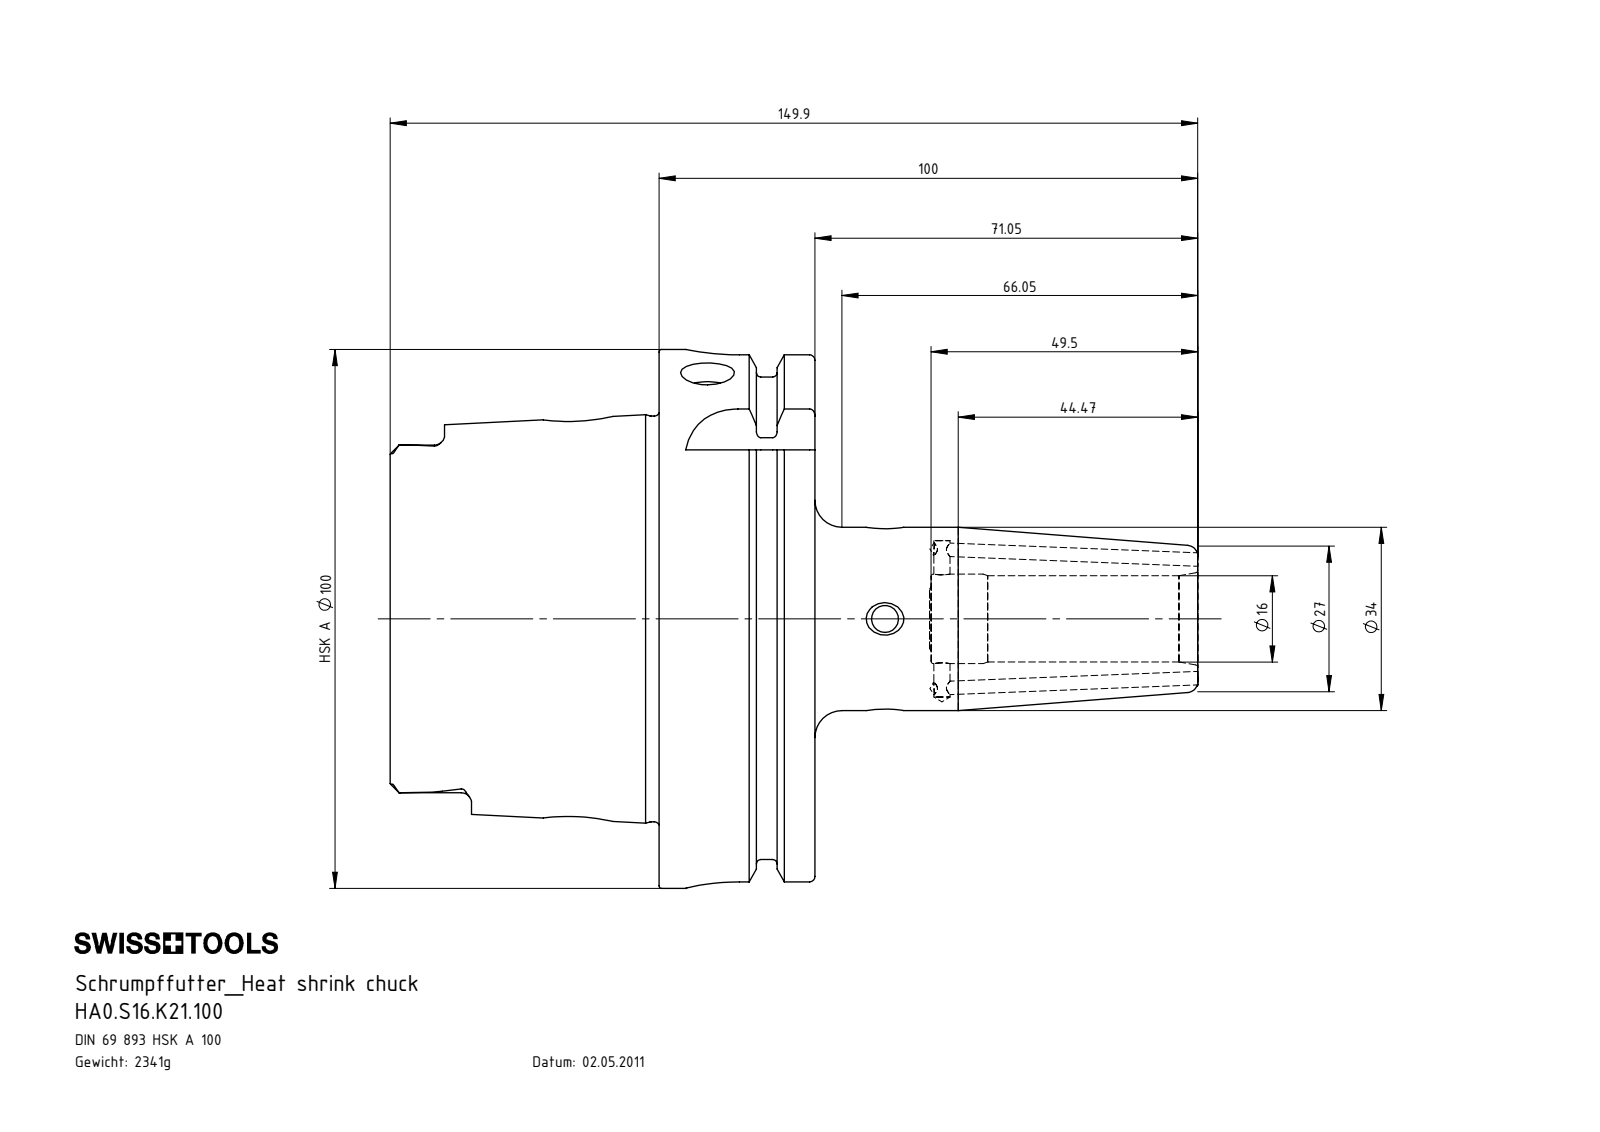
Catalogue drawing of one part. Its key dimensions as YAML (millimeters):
part_name: "ERU-CJ2.001.006; ERU-AN5.K01.020_A; HA0-S16.K21.100_C_Fertigbearbeitung; HA0.S16.K21.100"
step_written_by: "SolidWorks 2017 (AUTOMOTIVE_DESIGN)"
units: millimeters
bodies: {solids: 4, faces: 295, planar: 95, cylindrical: 84, other: 116}
overall_size: [149.98, 100, 100]
volume: 298223
surface_area: 62240
round_holes:
  - {diameter: 10, count: 3}
  - {diameter: 2.5, count: 2}
  - {diameter: 5, count: 2}
  - {diameter: 3, count: 1}
  - {diameter: 6, count: 1}
  - {diameter: 11, count: 1}
  - {diameter: 12, count: 1}
  - {diameter: 16, count: 1}
  - {diameter: 16.6, count: 1}
  - {diameter: 22.5, count: 1}
  - {diameter: 26, count: 1}
  - {diameter: 53, count: 1}
round_bosses_or_shafts:
  - {diameter: 3, count: 2}
  - {diameter: 100, count: 1}
  - {diameter: 91.95, count: 1}
  - {diameter: 75.26, count: 1}
  - {diameter: 34, count: 1}
  - {diameter: 12, count: 1}
partial_cylinders:
  - {radius: 1.9, count: 6}
  - {radius: 4.88, count: 4}
  - {radius: 10, count: 4}
face_to_face_distances: [28.95, 12.45, 16.5, 49.9, 62.35, 78.85, 87.8, 78.2, 28.3, 15.85]
hole_center_spacings: [10.55, 34.95, 56.95, 67.5]
